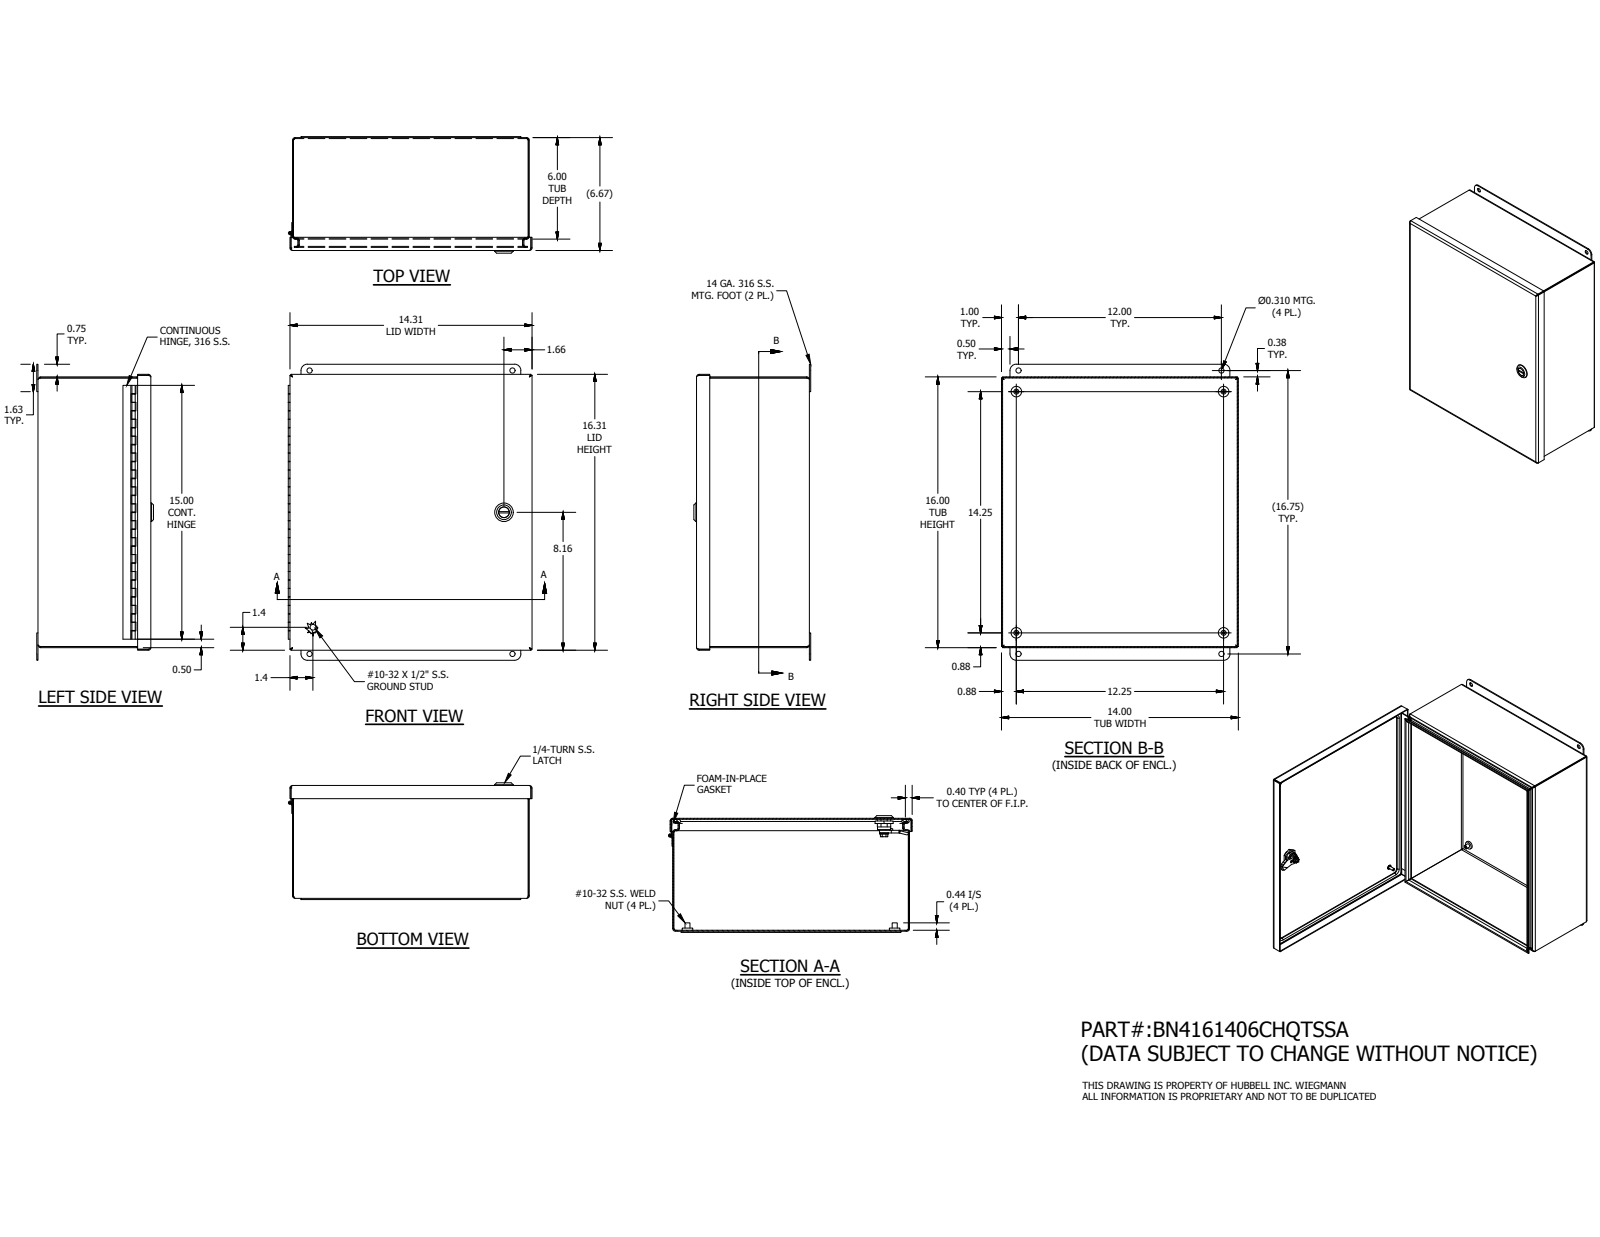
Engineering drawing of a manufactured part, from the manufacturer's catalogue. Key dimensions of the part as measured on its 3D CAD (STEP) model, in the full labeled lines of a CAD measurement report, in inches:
Part name (STEP PRODUCT): BN41614CHQTSSALID; 16x14; 348132; 32886LH (+8 more)
STEP written by: Autodesk Inventor 2016 (AUTOMOTIVE_DESIGN)
Units: inches
Bodies: 21 solids, 711 faces (390 planar, 224 cylindrical, 97 other)
Overall size (bounding box): 17.5 × 14.412 × 6.905
Volume: 63.59 in³ · Surface area: 2 041 in²
Round holes (diameter × count): ⌀0.156 ×4, ⌀0.31 ×4, ⌀0.117 ×1, ⌀0.197 ×1, ⌀0.315 ×1, ⌀0.394 ×1, ⌀0.402 ×1, ⌀0.634 ×1, ⌀0.802 ×1
Round bosses / shafts (diameter × count): ⌀0.625 ×4, ⌀0.3 ×4, ⌀1.102 ×1, ⌀0.78 ×1, ⌀0.63 ×1, ⌀0.598 ×1, ⌀0.531 ×1, ⌀0.504 ×1
Partial cylindrical surfaces — rounded edges, fillets, slot ends (radius × count): R0.094 ×20, R0.153 ×20, R0.125 ×16, R0.02 ×8, R0.157 ×4, R0.375 ×4, R0.091 ×2, R0.254 ×1
Main face-to-face distances: 0.059, 0.059, 6.614, 6.672, 6.555, 6.613, 15.941, 13.882, 13.941, 13.941
Hole centre spacings: 1.256, 15.5, 19.679, 12, 12.189, 12.189, 12.25, 13.635
